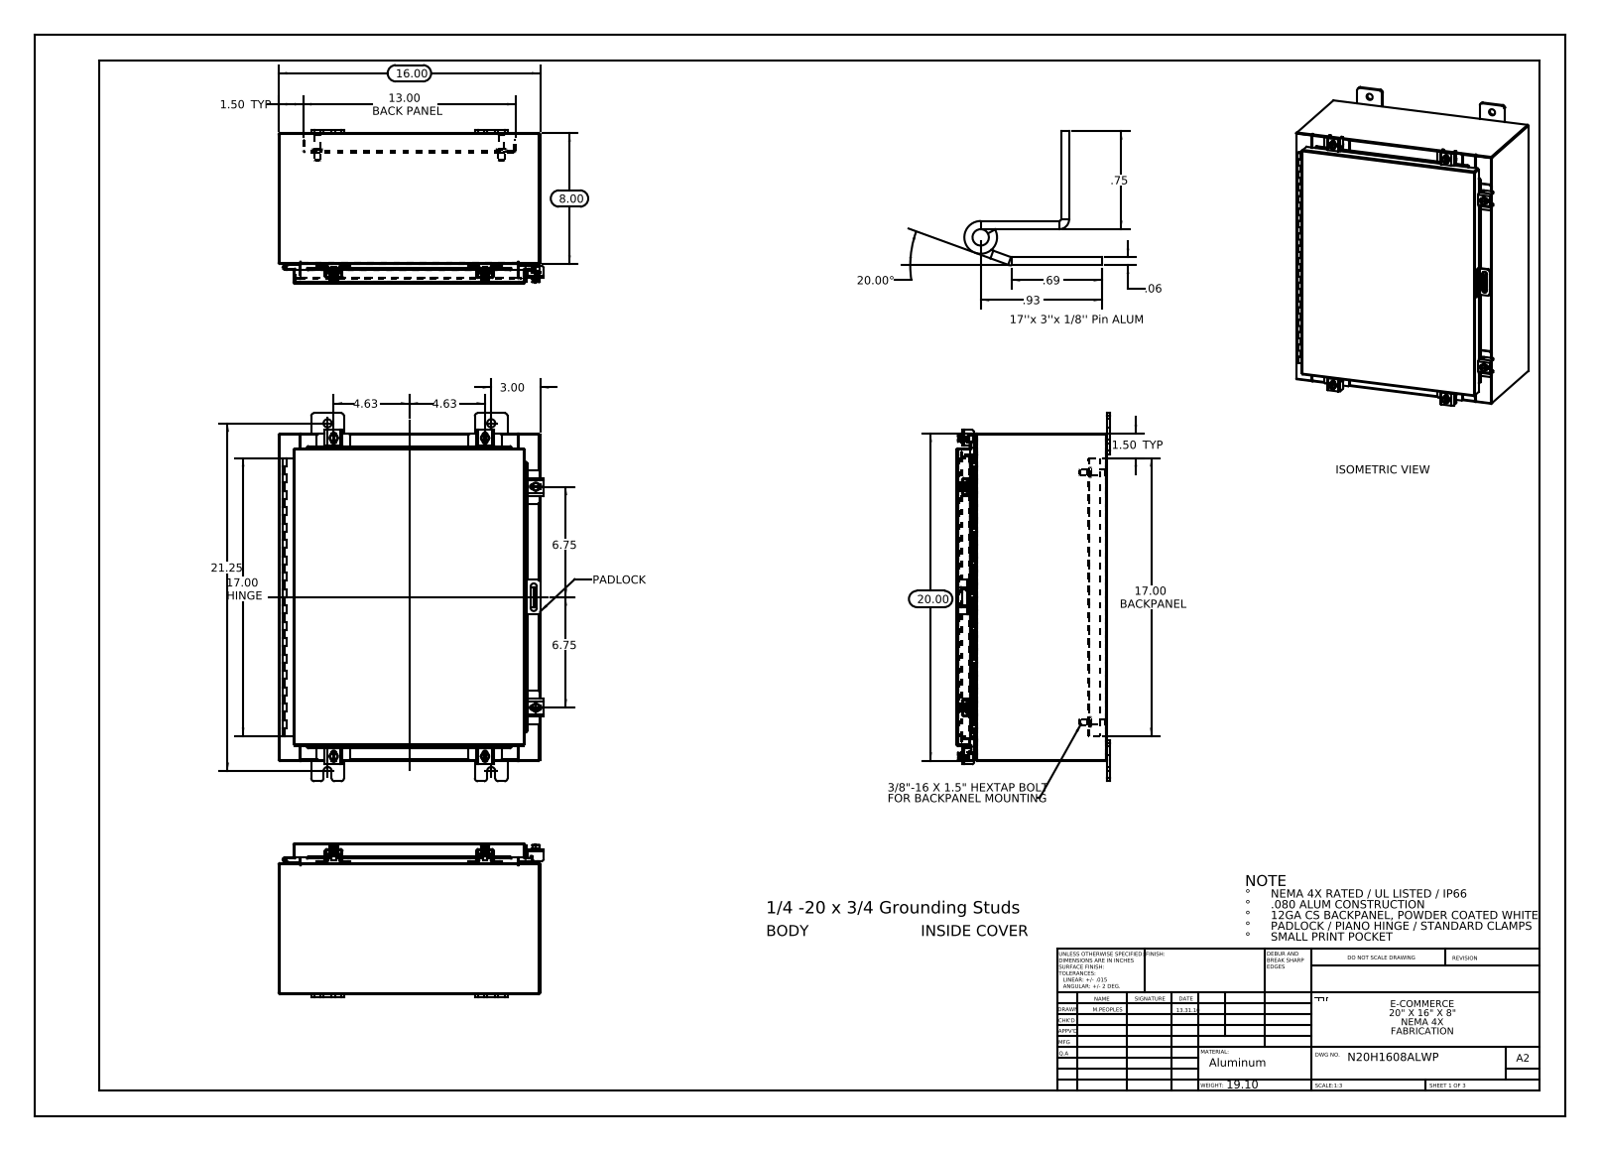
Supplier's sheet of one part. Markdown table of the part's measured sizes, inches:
| quantity | value |
| --- | --- |
| part name | N20H1608ALWP Top; N20H1608ALWP 125 Pin Hinge; N20H1608ALWP 22104005_DEFAULT; N20H1608ALWP Padlock Hasp (+8 more) |
| STEP written by | SolidWorks 2013 (CONFIG_CONTROL_DESIGN) |
| units | inches |
| bodies | 47 solids, 1613 faces (860 planar, 657 cylindrical, 96 other) |
| overall size | 22.5 × 16.211 × 9.389 |
| volume | 135.6 in³ |
| surface area | 3 435 in² |
| round holes (diameter × count) | 0.5 × 8, 0.213 × 6, 0.26 × 6, 0.125 × 2, 0.125 × 1 |
| round bosses / shafts (diameter × count) | 0.25 × 7, 0.5 × 6, 0.399 × 6, 0.625 × 4, 0.375 × 4, 0.33 × 4 |
| partial cylindrical surfaces (radius × count) | 0.06 × 30, 0.013 × 25, 0.19 × 24, 0.088 × 21, 0.12 × 12, 0.141 × 12, 0.125 × 10, 0.05 × 9 |
| main face-to-face distances | 0.075, 9.126, 15.925, 9.201, 9.051, 19.925, 0.104, 1, 1.075, 8.051 |
| hole center spacings | 17.38, 1.858, 2.276, 2.326, 2.326, 3.065, 4.297, 9.25 |
